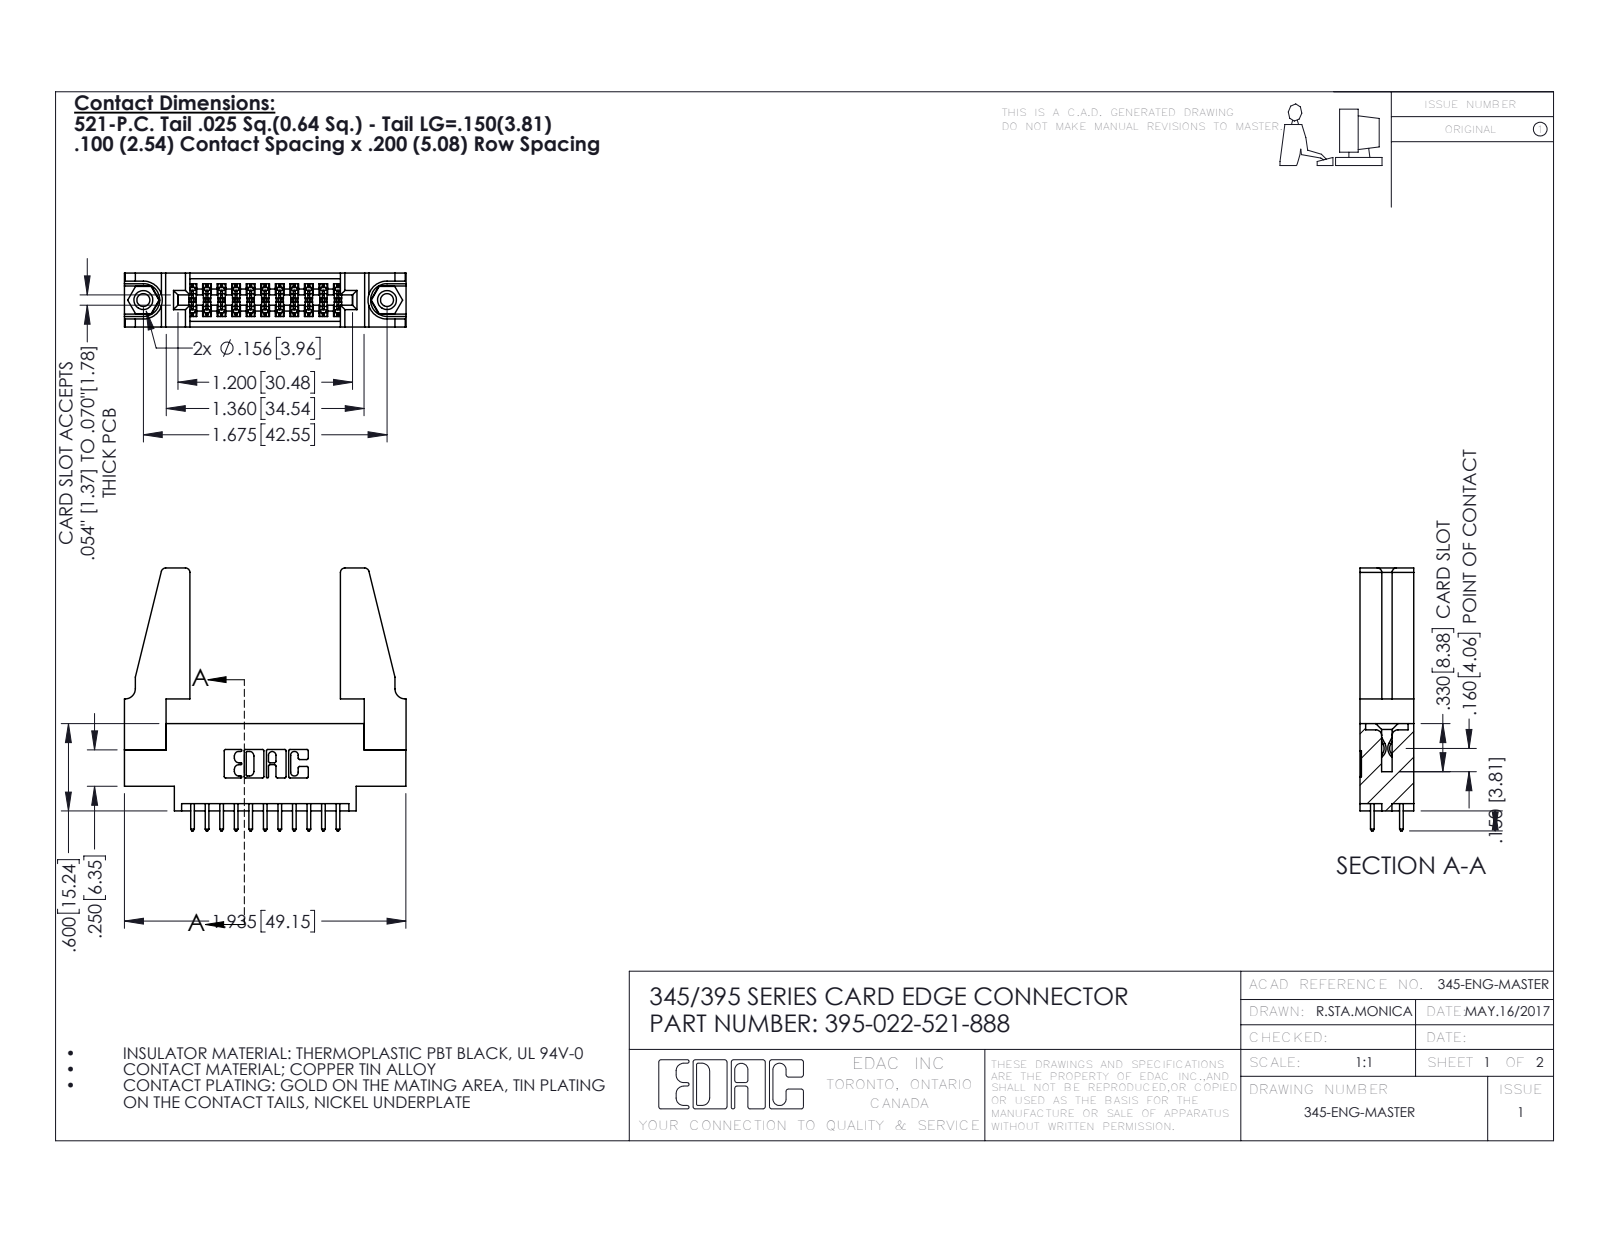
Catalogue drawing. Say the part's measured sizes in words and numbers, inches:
The part is named "345-292-001_345-293-121; 395-022-521-888; 345 Part_0.170 Offset - 0.156 Dia-TH; 345-220-078_345-220-088 (+1 more)". Its 3-D file was written by "SolidWorks 2016 (CONFIG_CONTROL_DESIGN)". It is 27 solids with 1354 faces: 882 planar, 456 cylindrical and 16 other. Overall it measures 1.936 by 1.807 by 0.37 inches. Its volume is 0.465 cubic inches and its surface area 14.05 square inches. Round holes: 2 of diameter 0.089, 2 of diameter 0.125, 2 of diameter 0.156, 1 of diameter 0.064. Round bosses or shafts: 2 of diameter 0.155. Partial cylindrical surfaces (rounded edges, fillets, slot ends): 33 of radius 0.006, 22 of radius 0.01, 22 of radius 0.01, 8 of radius 0.03, 6 of radius 0.007, 6 of radius 0.031, 3 of radius 0.026, 2 of radius 0.014. The main face-to-face distances are 0.37, 0.072, 0.298, 0.2, 0.098, 0.272, 0.025, 0.225, 0.175, 0.148. The hole center spacings are 0.27, 1.443, 1.675.
